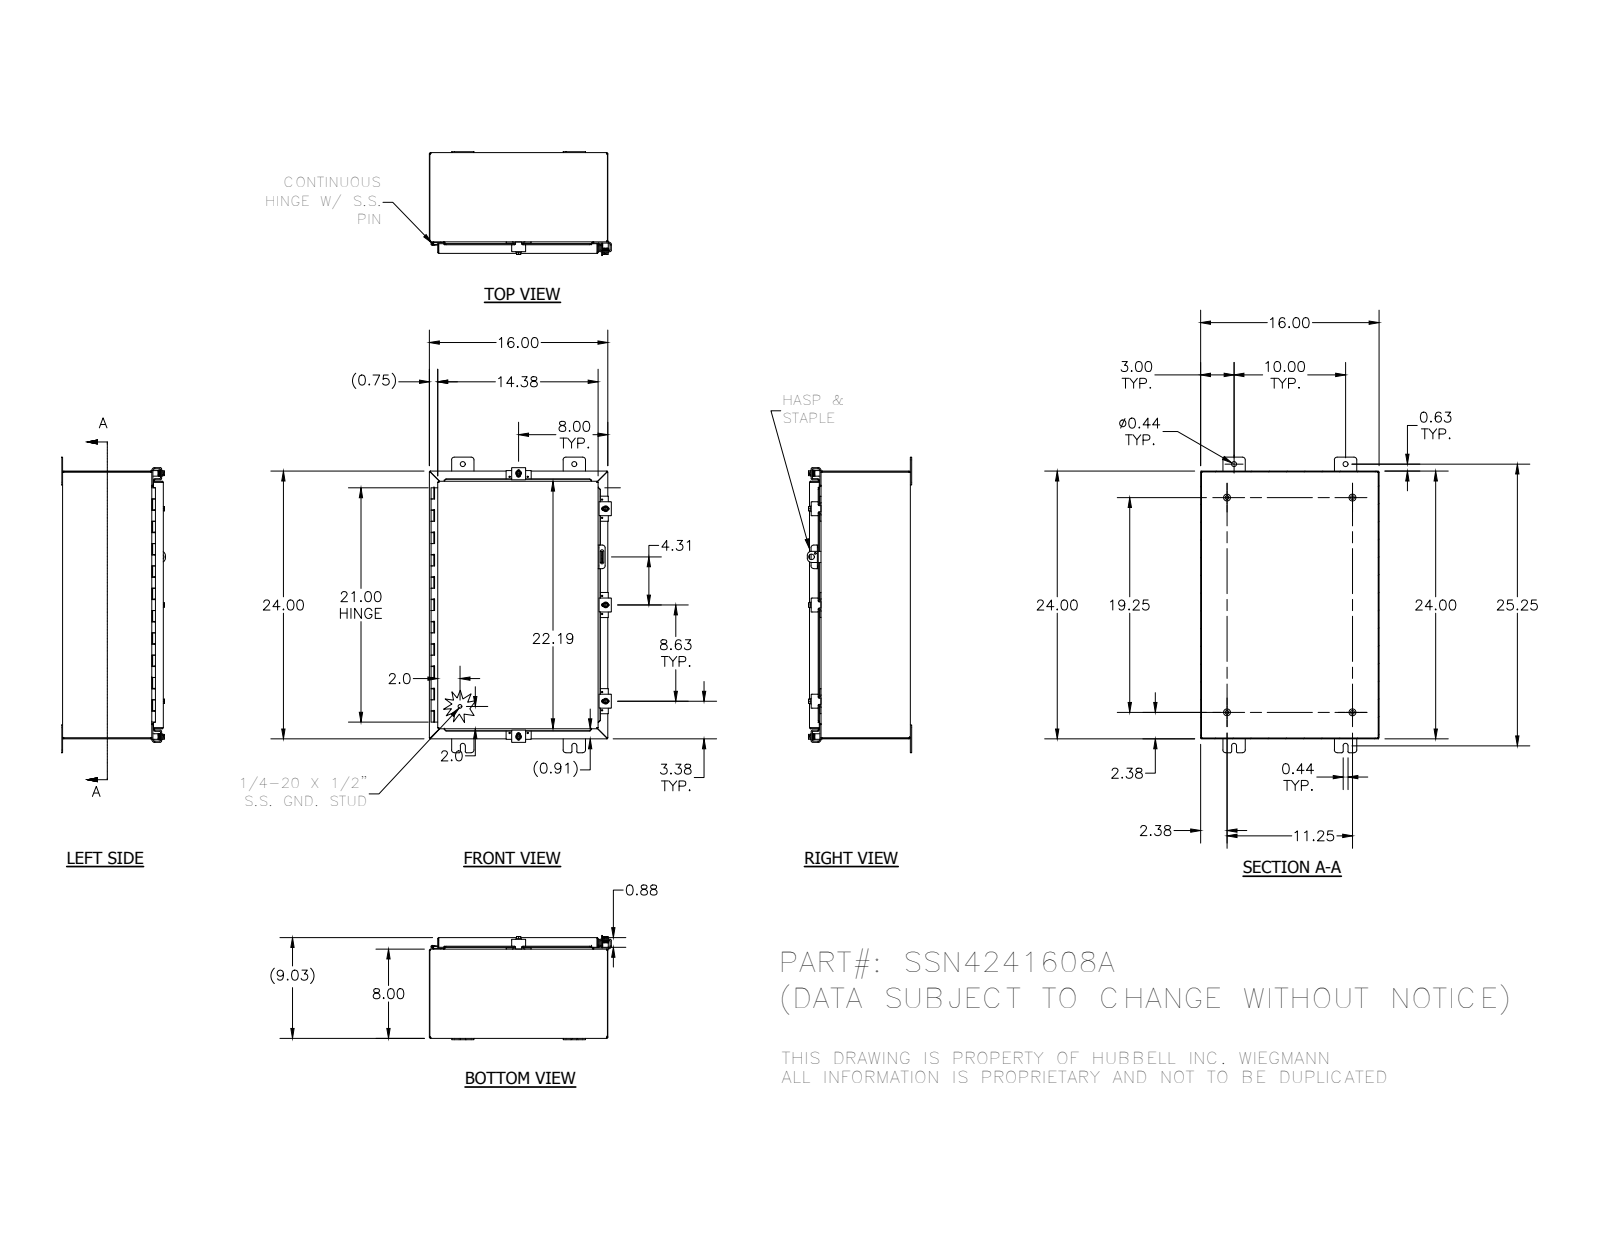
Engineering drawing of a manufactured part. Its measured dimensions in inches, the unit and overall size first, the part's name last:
Units: inches
Overall size (bounding box): 26.5 × 16.216 × 9.355
Round holes (diameter × count): ⌀0.11 ×10, ⌀0.211 ×5, ⌀0.281 ×5, ⌀0.3 ×5, ⌀0.438 ×4, ⌀0.125 ×1, ⌀0.156 ×1, ⌀0.5 ×1
Round bosses / shafts (diameter × count): ⌀0.25 ×7, ⌀0.52 ×5, ⌀0.5 ×5, ⌀0.35 ×5, ⌀0.625 ×4, ⌀0.33 ×4, ⌀0.337 ×1, ⌀0.12 ×1
Partial cylindrical surfaces — rounded edges, fillets, slot ends (radius × count): R0.03 ×61, R0.125 ×35, R0.25 ×31, R0.031 ×23, R0.105 ×23, R0.062 ×16, R0.141 ×10, R0.07 ×8
Main face-to-face distances: 0.074, 8.959, 15.926, 8.885, 9.033, 23.926, 7.926, 1.033, 16, 15.852
Hole centre spacings: 0.876, 23.303, 1.625, 7.82, 8.625, 8.625, 9.443, 17.25
Volume: 131.9 in³ · Surface area: 3 452 in²
Bodies: 42 solids, 1656 faces (660 planar, 713 cylindrical, 283 other)
Part name (STEP PRODUCT): 32874-24L; 30824-1; 32874-24T; SSN4241608ABKP (+8 more)
STEP written by: SolidWorks 2014 (AUTOMOTIVE_DESIGN)
